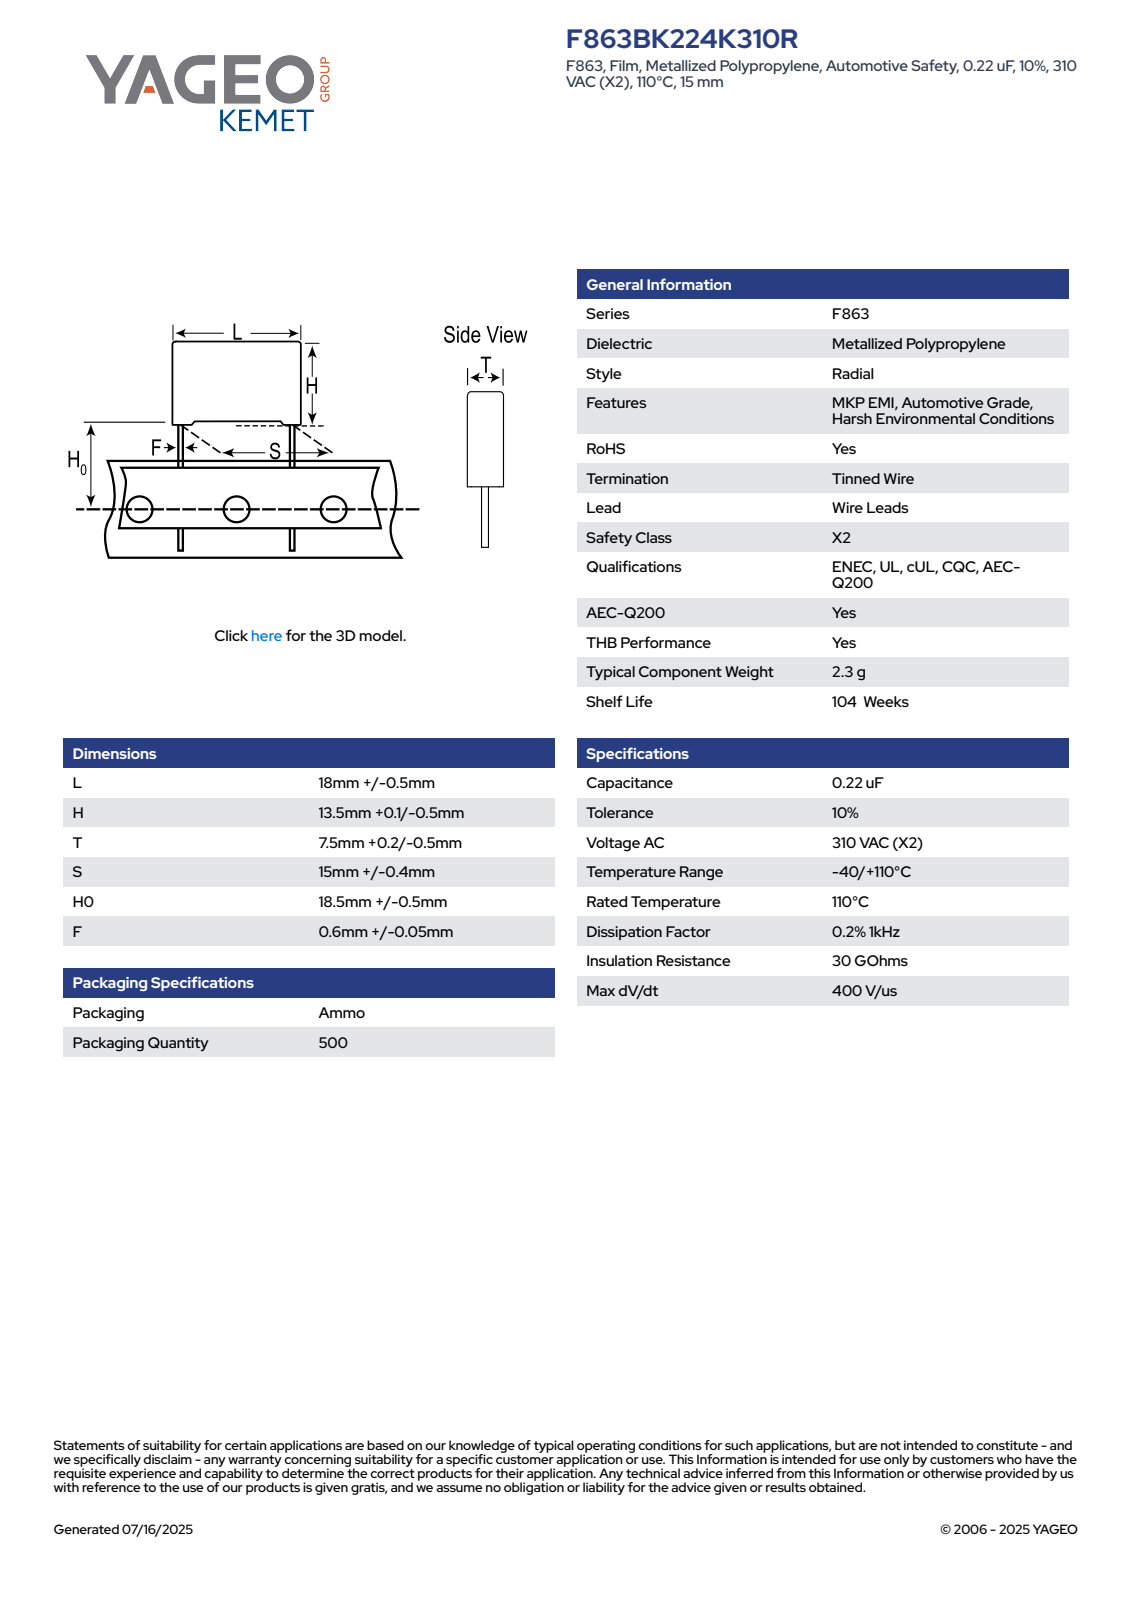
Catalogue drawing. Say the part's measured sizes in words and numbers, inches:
The part is named "CFR_RB2_18X13.5X7.5_L18.5H13.6T7.7S15H019F0.65". Its 3-D file was written by "SolidWorks 2020 (AUTOMOTIVE_DESIGN)". It is 4 solids with 85 faces: 77 planar, 8 cylindrical and 0 other. Overall it measures 1.283 by 0.728 by 0.304 inches. Its volume is 0.113 cubic inches and its surface area 1.716 square inches. Round bosses or shafts: 2 of diameter 0.026. Partial cylindrical surfaces (rounded edges, fillets, slot ends): 4 of radius 0.02. The main face-to-face distances are 0.303, 0.506, 0.728, 0.024, 0.03, 0.535, 0.279, 0.019, 0.517, 0.704.
